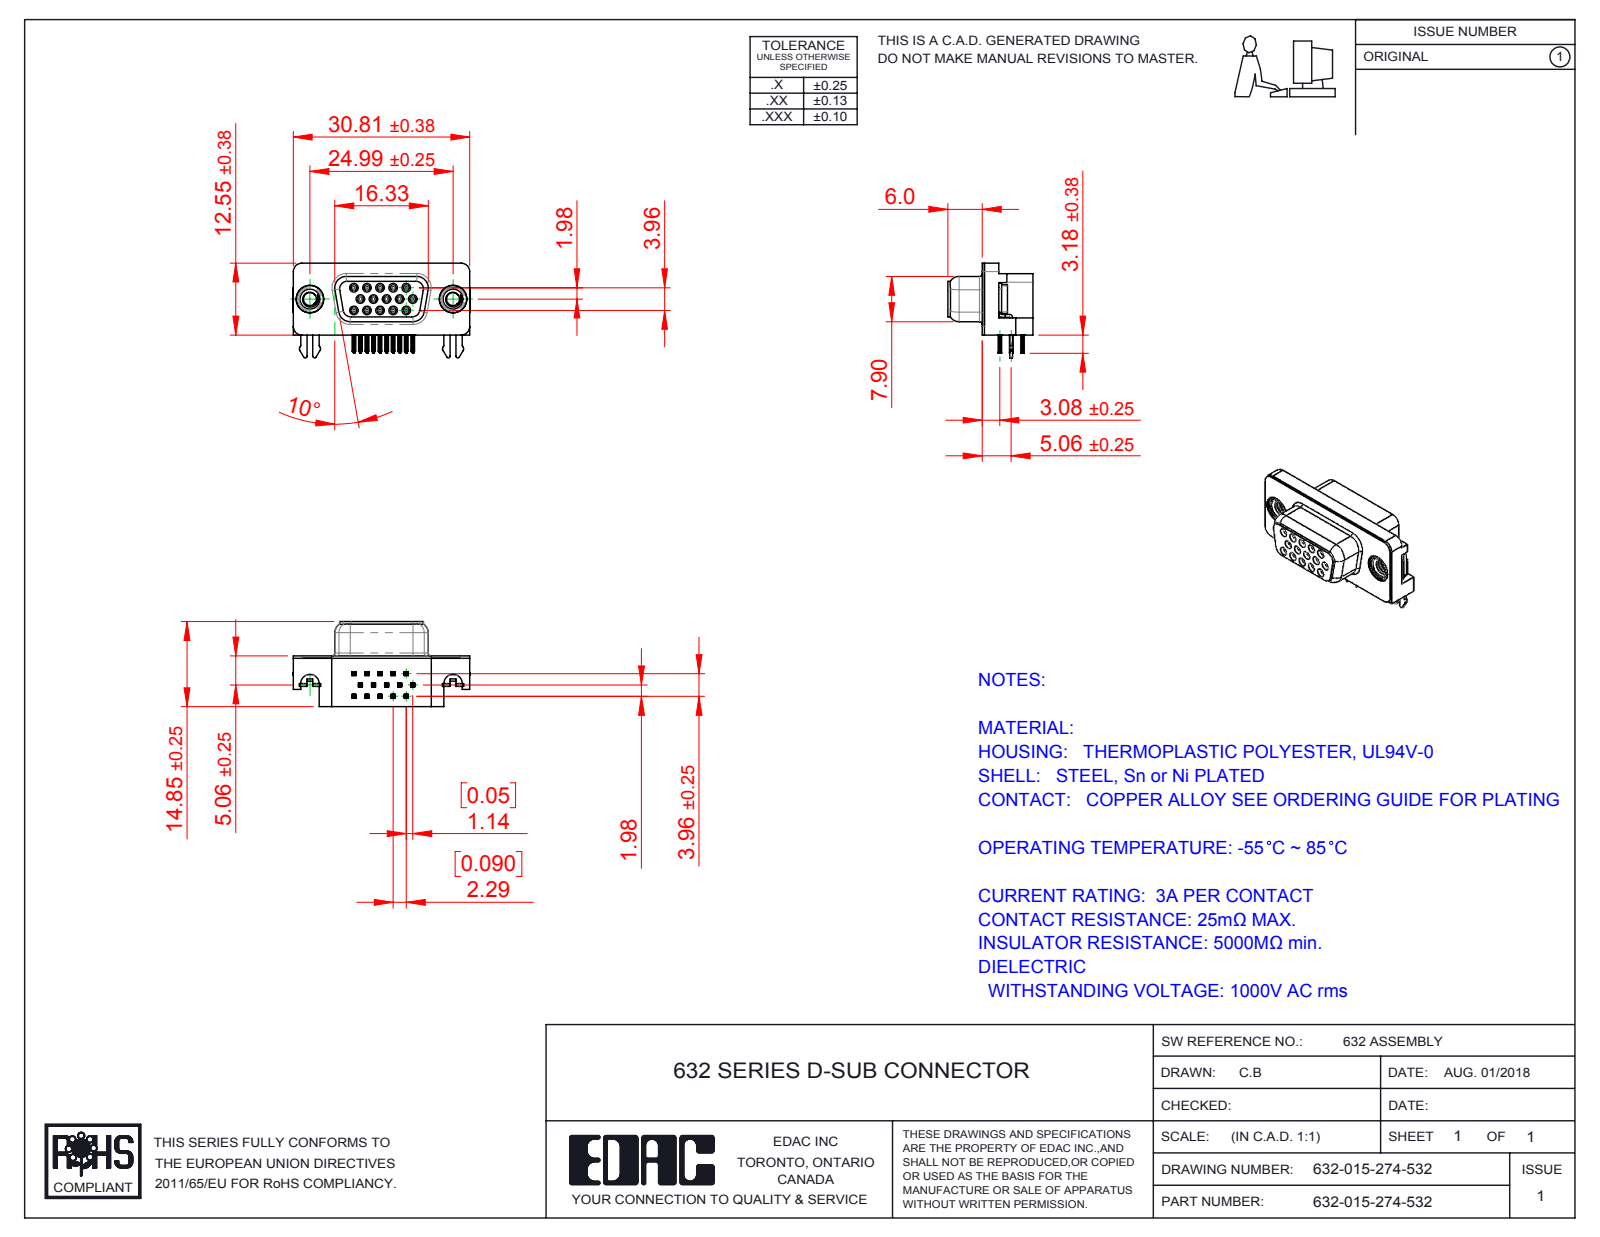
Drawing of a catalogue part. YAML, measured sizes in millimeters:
part_name: "632 4-40 Threaded Rivet; 632-015-274-502; 632 Housing_15 Socket; 632 Shell_9 Socket (+5 more)"
step_written_by: "SolidWorks 2016 (CONFIG_CONTROL_DESIGN)"
units: millimeters
bodies: {solids: 21, faces: 2338, planar: 990, cylindrical: 612, other: 736}
overall_size: [30.89, 16.55, 14.85]
volume: 2921
surface_area: 5015
round_holes:
  - {diameter: 0.8, count: 15}
  - {diameter: 0.9, count: 15}
  - {diameter: 2.26, count: 2}
  - {diameter: 4, count: 2}
  - {diameter: 4.8, count: 2}
  - {diameter: 5, count: 2}
round_bosses_or_shafts:
  - {diameter: 1.2, count: 15}
  - {diameter: 4.9, count: 2}
  - {diameter: 4.75, count: 2}
  - {diameter: 3.9, count: 2}
partial_cylinders:
  - {radius: 0.1, count: 120}
  - {radius: 0.15, count: 60}
  - {radius: 0.35, count: 30}
  - {radius: 0.34, count: 15}
  - {radius: 1, count: 11}
  - {radius: 0.28, count: 10}
  - {radius: 0.5, count: 10}
  - {radius: 0.25, count: 8}
face_to_face_distances: [0.4, 1.98, 8.45, 8.85, 2.9, 2.5, 5.95, 6.4, 6.7, 7.05]
hole_center_spacings: [2.28, 2.29, 3.96, 4.57, 6.05, 3.97, 4.58, 6.86]
